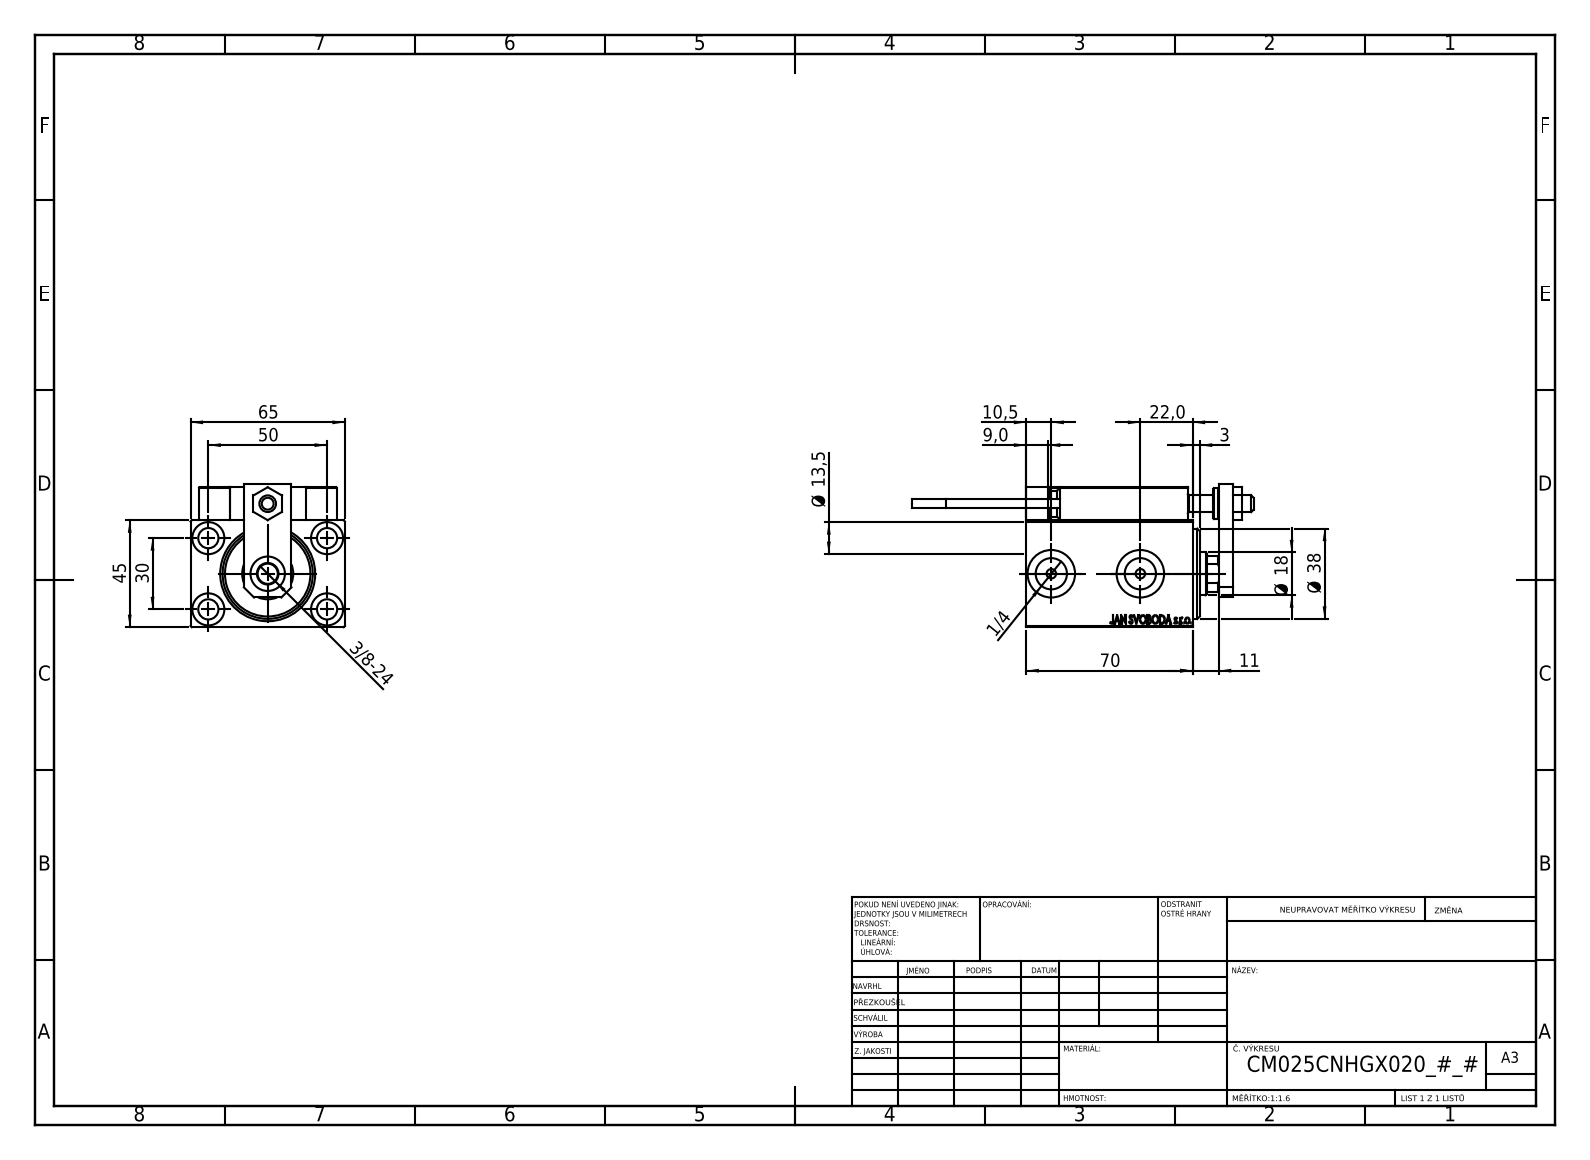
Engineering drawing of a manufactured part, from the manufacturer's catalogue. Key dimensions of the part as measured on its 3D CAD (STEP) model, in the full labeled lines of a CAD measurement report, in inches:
Part name (STEP PRODUCT): ALLEN BOLT D5; TYC_L79; ZARAZKA; SWITCH X (+7 more)
STEP written by: SolidWorks 2019 (CONFIG_CONTROL_DESIGN)
Units: inches
Bodies: 23 solids, 1282 faces (560 planar, 188 cylindrical, 534 other)
Overall size (bounding box): 5.657 × 2.559 × 2.382
Volume: 13.62 in³ · Surface area: 107.2 in²
Round holes (diameter × count): ⌀0.157 ×6, ⌀0.315 ×5, ⌀0.335 ×5, ⌀0.126 ×4, ⌀0.531 ×4, ⌀0.197 ×2, ⌀0.518 ×2, ⌀0.787 ×2, ⌀0.276 ×1, ⌀0.571 ×1, ⌀0.709 ×1, ⌀0.846 ×1
Round bosses / shafts (diameter × count): ⌀0.197 ×2, ⌀0.15 ×2, ⌀0.512 ×1, ⌀0.433 ×1
Partial cylindrical surfaces — rounded edges, fillets, slot ends (radius × count): R0.012 ×30, R0.118 ×2, R0.335 ×1
Main face-to-face distances: 1.772, 2.323, 0.551, 2.559, 0.236, 0.118, 0.748, 0.197, 0.512, 0.276
Hole centre spacings: 1.148, 0.448, 0.787, 0.87, 1.138, 1.165, 1.169, 1.181
